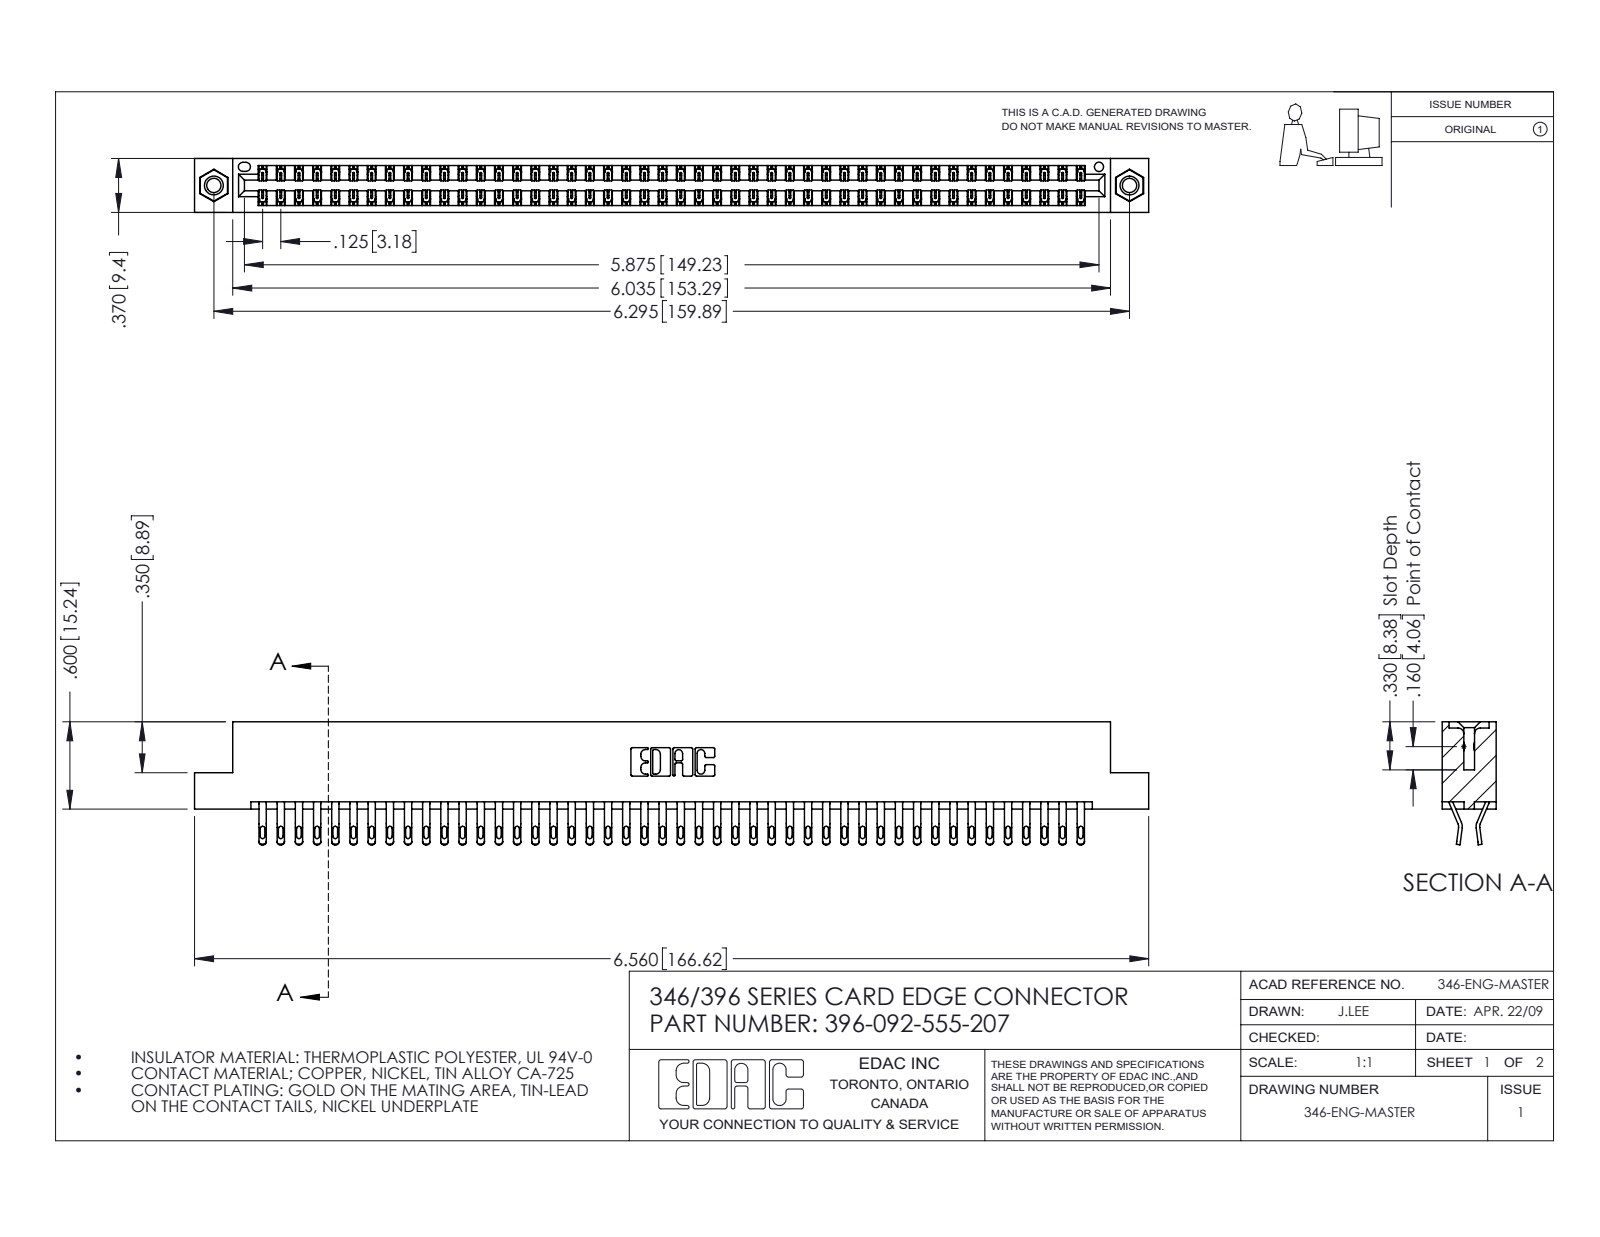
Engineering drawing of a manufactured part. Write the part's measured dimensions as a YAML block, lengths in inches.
part_name: "345-292-001_555 Tail; 396-092-555-207; 346 Part_Flush Mounting Lugs - 0.156 Dia-TI; 345-250-001_345-250-005-103"
step_written_by: "SolidWorks 2016 (CONFIG_CONTROL_DESIGN)"
units: inches
bodies: {solids: 95, faces: 5518, planar: 3144, cylindrical: 2358, other: 16}
overall_size: [6.56, 0.845, 0.37]
volume: 1.009
surface_area: 36.85
round_holes:
  - {diameter: 0.098, count: 2}
  - {diameter: 0.125, count: 2}
  - {diameter: 0.156, count: 2}
  - {diameter: 0.064, count: 1}
round_bosses_or_shafts:
  - {diameter: 0.155, count: 2}
partial_cylinders:
  - {radius: 0.016, count: 184}
  - {radius: 0.02, count: 184}
  - {radius: 0.006, count: 138}
  - {radius: 0.01, count: 22}
  - {radius: 0.007, count: 6}
  - {radius: 0.031, count: 6}
  - {radius: 0.026, count: 3}
  - {radius: 0.01, count: 2}
face_to_face_distances: [0.048, 0.322, 0.37, 0.25, 0.025, 0.072, 0.298, 0.275, 0.148, 0.222]
hole_center_spacings: [0.246, 6.086, 6.295]
